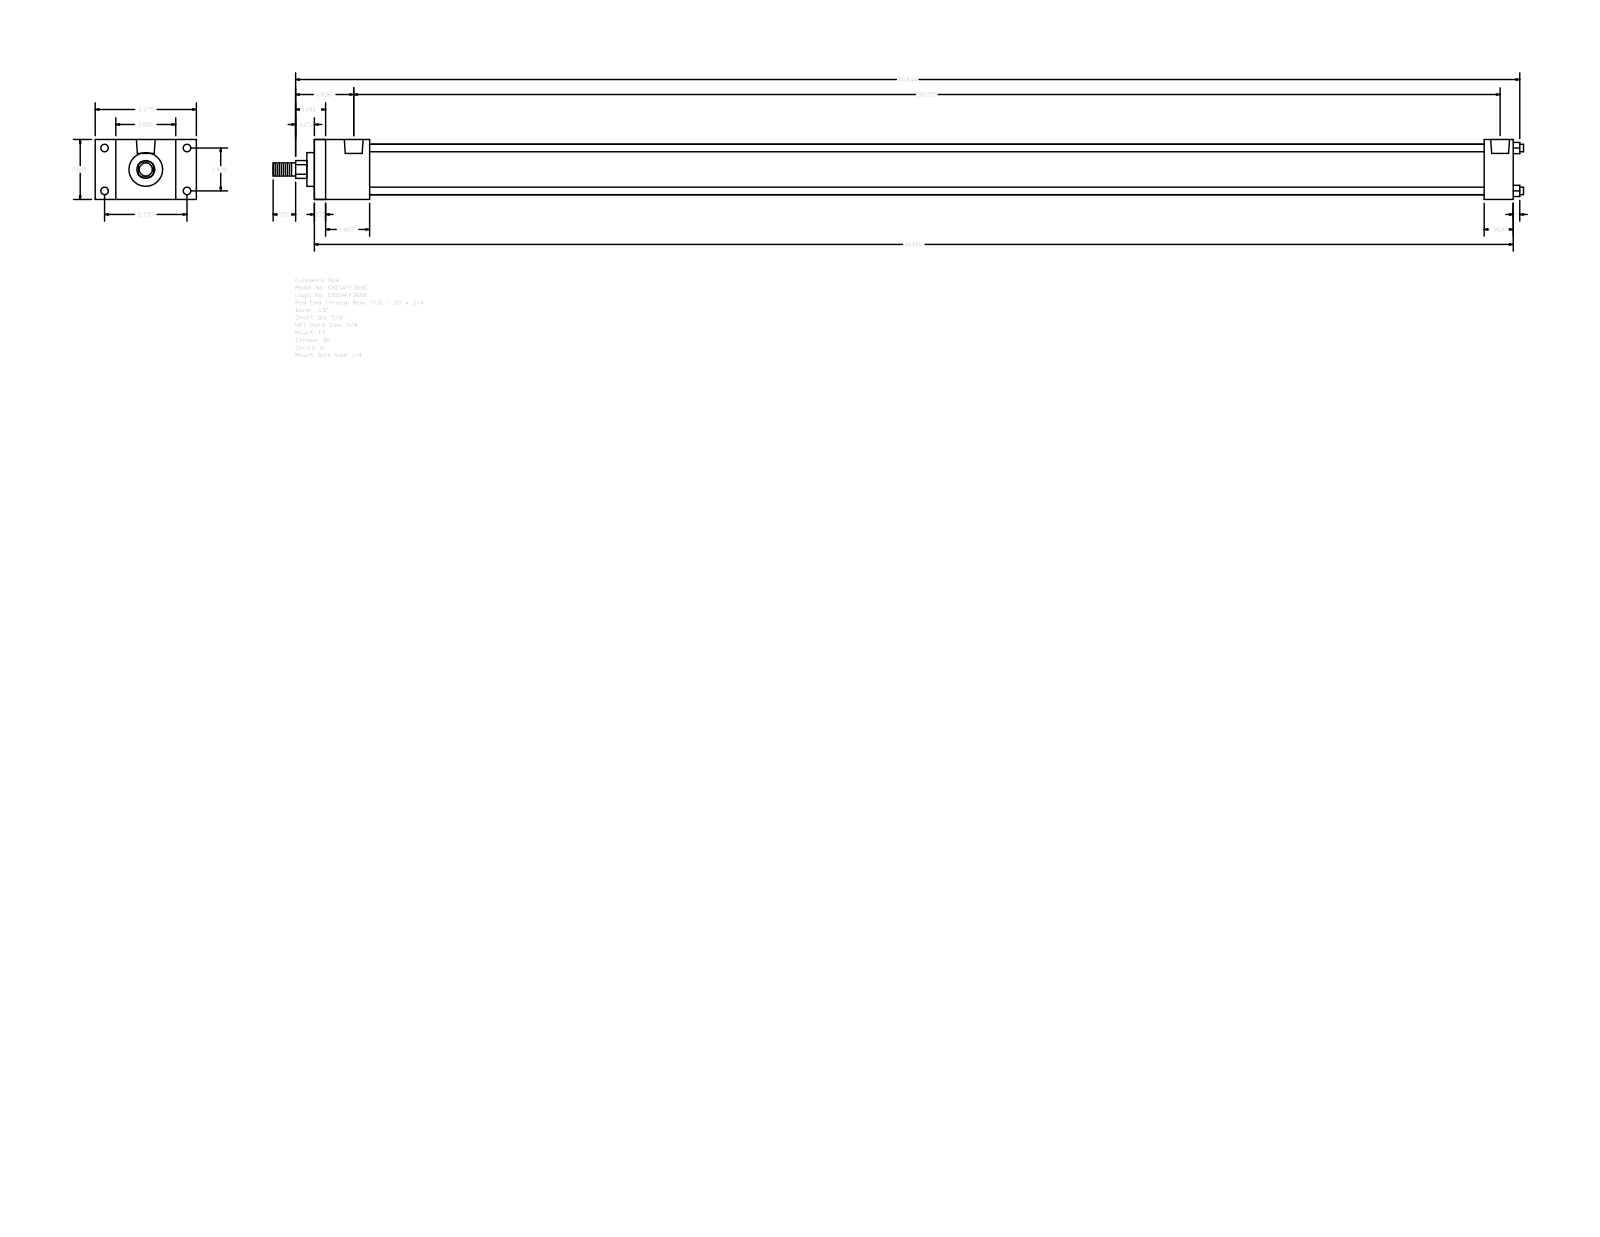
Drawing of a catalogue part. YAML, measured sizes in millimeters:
part_name: "A_FF__0150_0.625"
step_written_by: "GSSL Pune (CONFIG_CONTROL_DESIGN)"
units: millimeters
bodies: {solids: 0, faces: 92, planar: 64, cylindrical: 28, other: 0}
overall_size: [1059.66, 85.72, 50.8]
round_holes:
  - {diameter: 5.56, count: 4}
  - {diameter: 6.35, count: 4}
  - {diameter: 15.93, count: 2}
round_bosses_or_shafts:
  - {diameter: 6.35, count: 4}
  - {diameter: 42.93, count: 1}
  - {diameter: 28.57, count: 1}
  - {diameter: 15.88, count: 1}
  - {diameter: 11.11, count: 1}
partial_cylinders:
  - {radius: 7.54, count: 1}
face_to_face_distances: [50.8, 1016, 9.52, 1006.48, 46.83, 991.39, 37.31, 981.87, 944.56, 969.17]
hole_center_spacings: [3.97, 36.32, 69.84, 78.72, 963.61, 967.58, 971.55]
